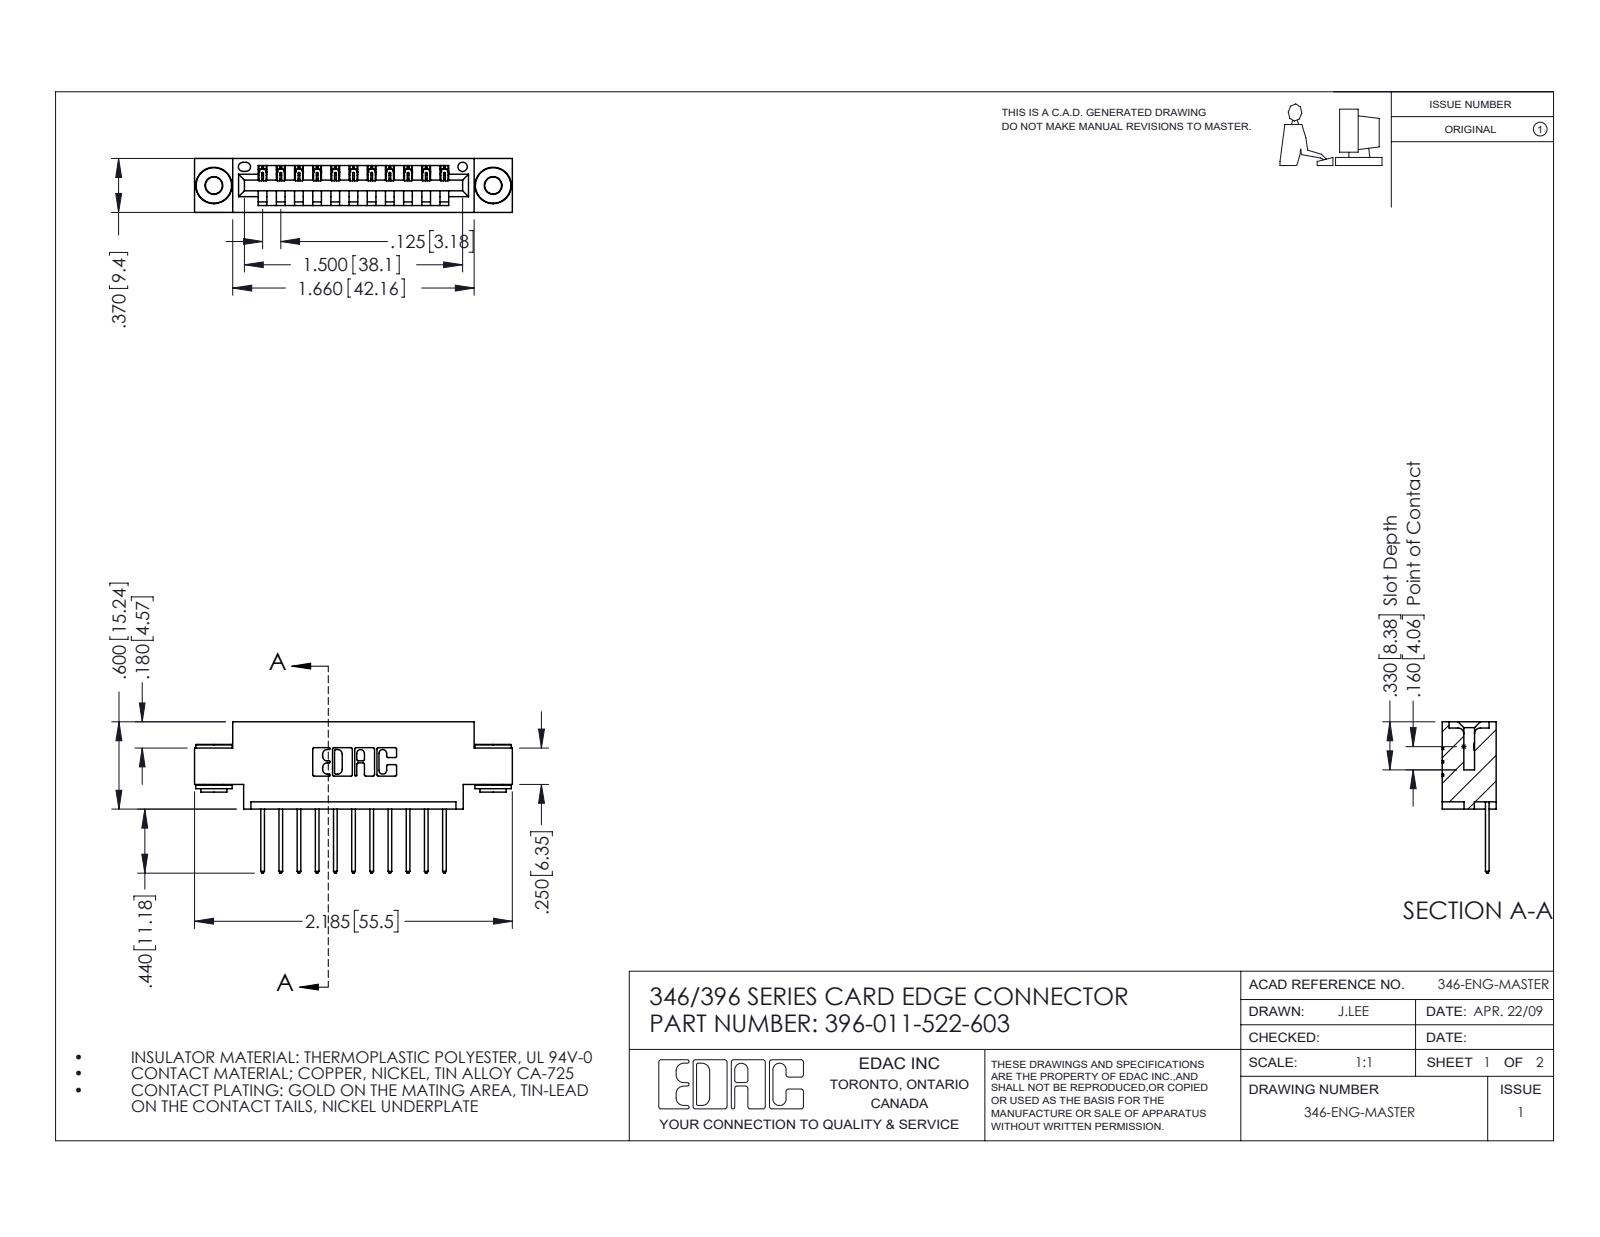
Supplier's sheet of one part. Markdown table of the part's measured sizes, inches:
| quantity | value |
| --- | --- |
| part name | 345-292-001_345-293-122; 345-250-002_345-250-002-102; 346 Part_0.170 Offset - 0.156 Dia-TH; 396-011-522-603 |
| STEP written by | SolidWorks 2016 (CONFIG_CONTROL_DESIGN) |
| units | inches |
| bodies | 14 solids, 802 faces (530 planar, 264 cylindrical, 8 other) |
| overall size | 2.185 × 1.04 × 0.37 |
| volume | 0.303 in³ |
| surface area | 9.751 in² |
| round holes (diameter × count) | 0.116 × 2, 0.156 × 2, 0.064 × 1 |
| round bosses / shafts (diameter × count) | 0.25 × 2, 0.18 × 2, 0.136 × 2 |
| partial cylindrical surfaces (radius × count) | 0.006 × 22, 0.01 × 22, 0.01 × 22, 0.007 × 6, 0.031 × 6, 0.026 × 3, 0.031 × 2, 0.04 × 2 |
| main face-to-face distances | 0.25, 0.37, 0.048, 0.322, 0.025, 0.072, 0.298, 0.148, 0.222, 0.1 |
| hole center spacings | 0.246, 1.715, 1.92 |
